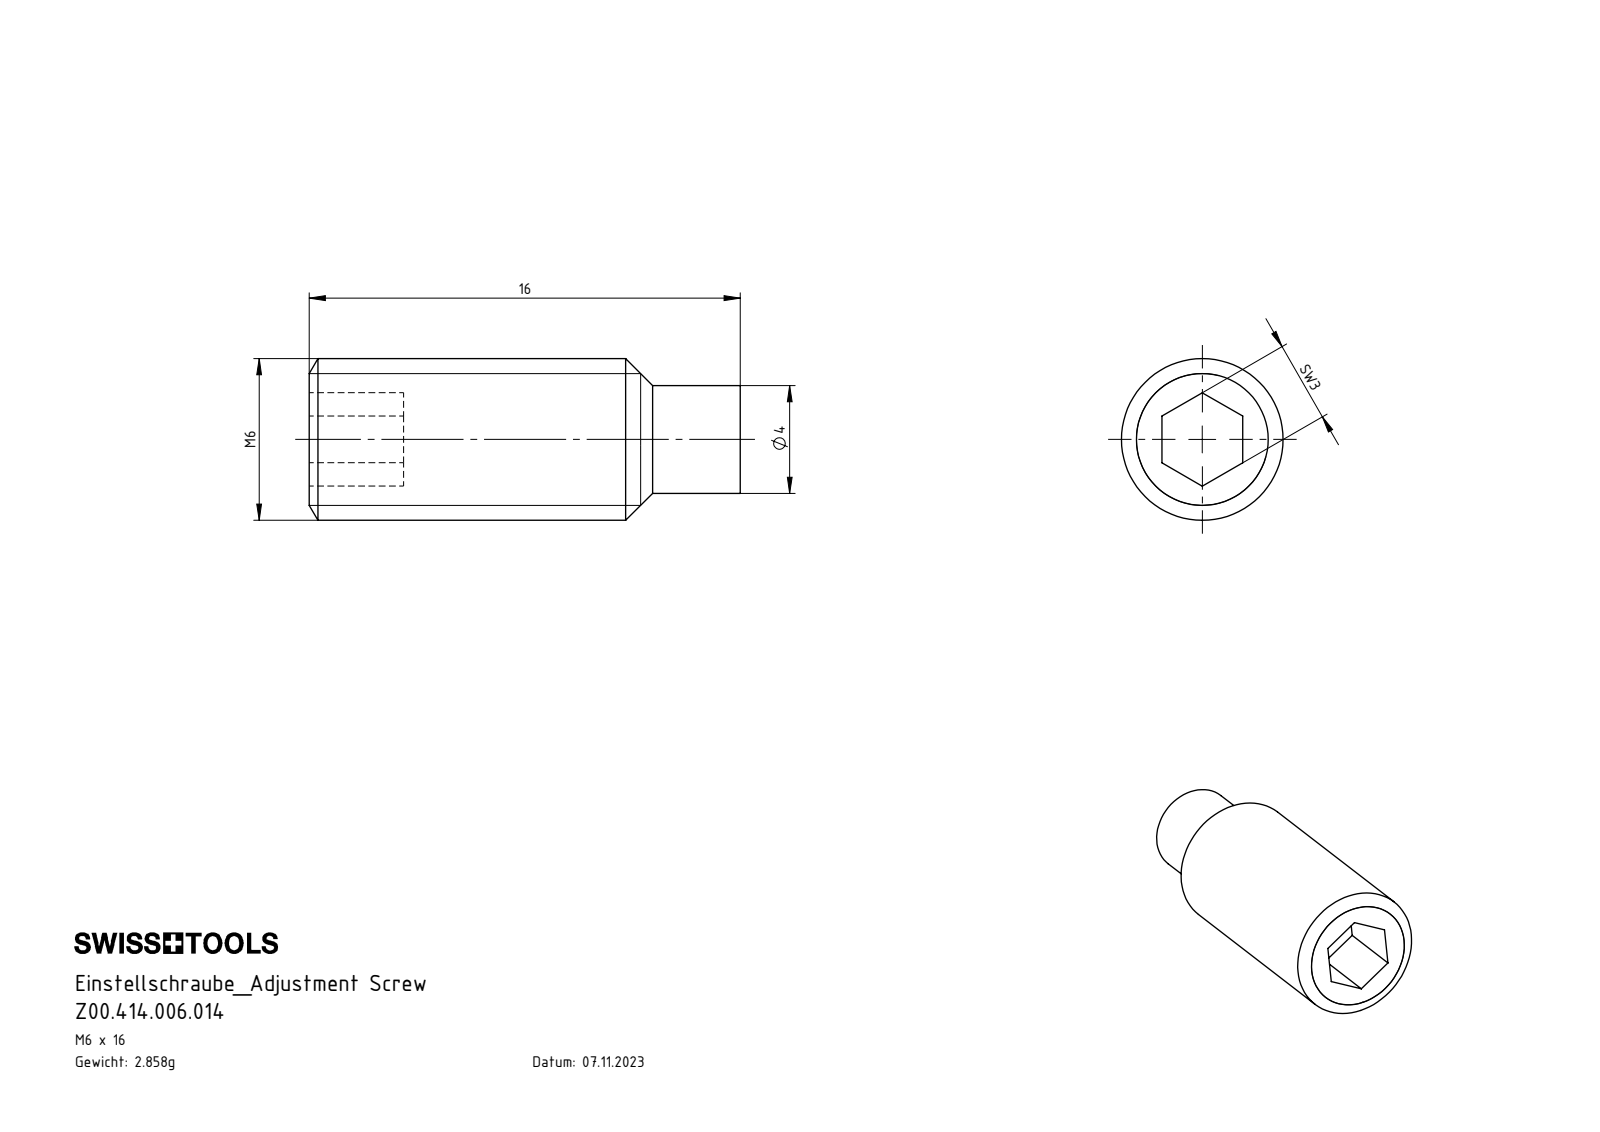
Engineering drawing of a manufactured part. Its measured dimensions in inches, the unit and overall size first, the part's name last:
Units: inches
Overall size (bounding box): 0.63 × 0.236 × 0.236
Round bosses / shafts (diameter × count): ⌀0.236 ×1, ⌀0.157 ×1
Main face-to-face distances: 0.118, 0.63, 0.138, 0.492
Volume: 0.022 in³ · Surface area: 0.553 in²
Bodies: 1 solid, 17 faces (9 planar, 4 cylindrical, 4 other)
Part name (STEP PRODUCT): Z00.414.006.014
STEP written by: SolidWorks 2022 (AUTOMOTIVE_DESIGN)
